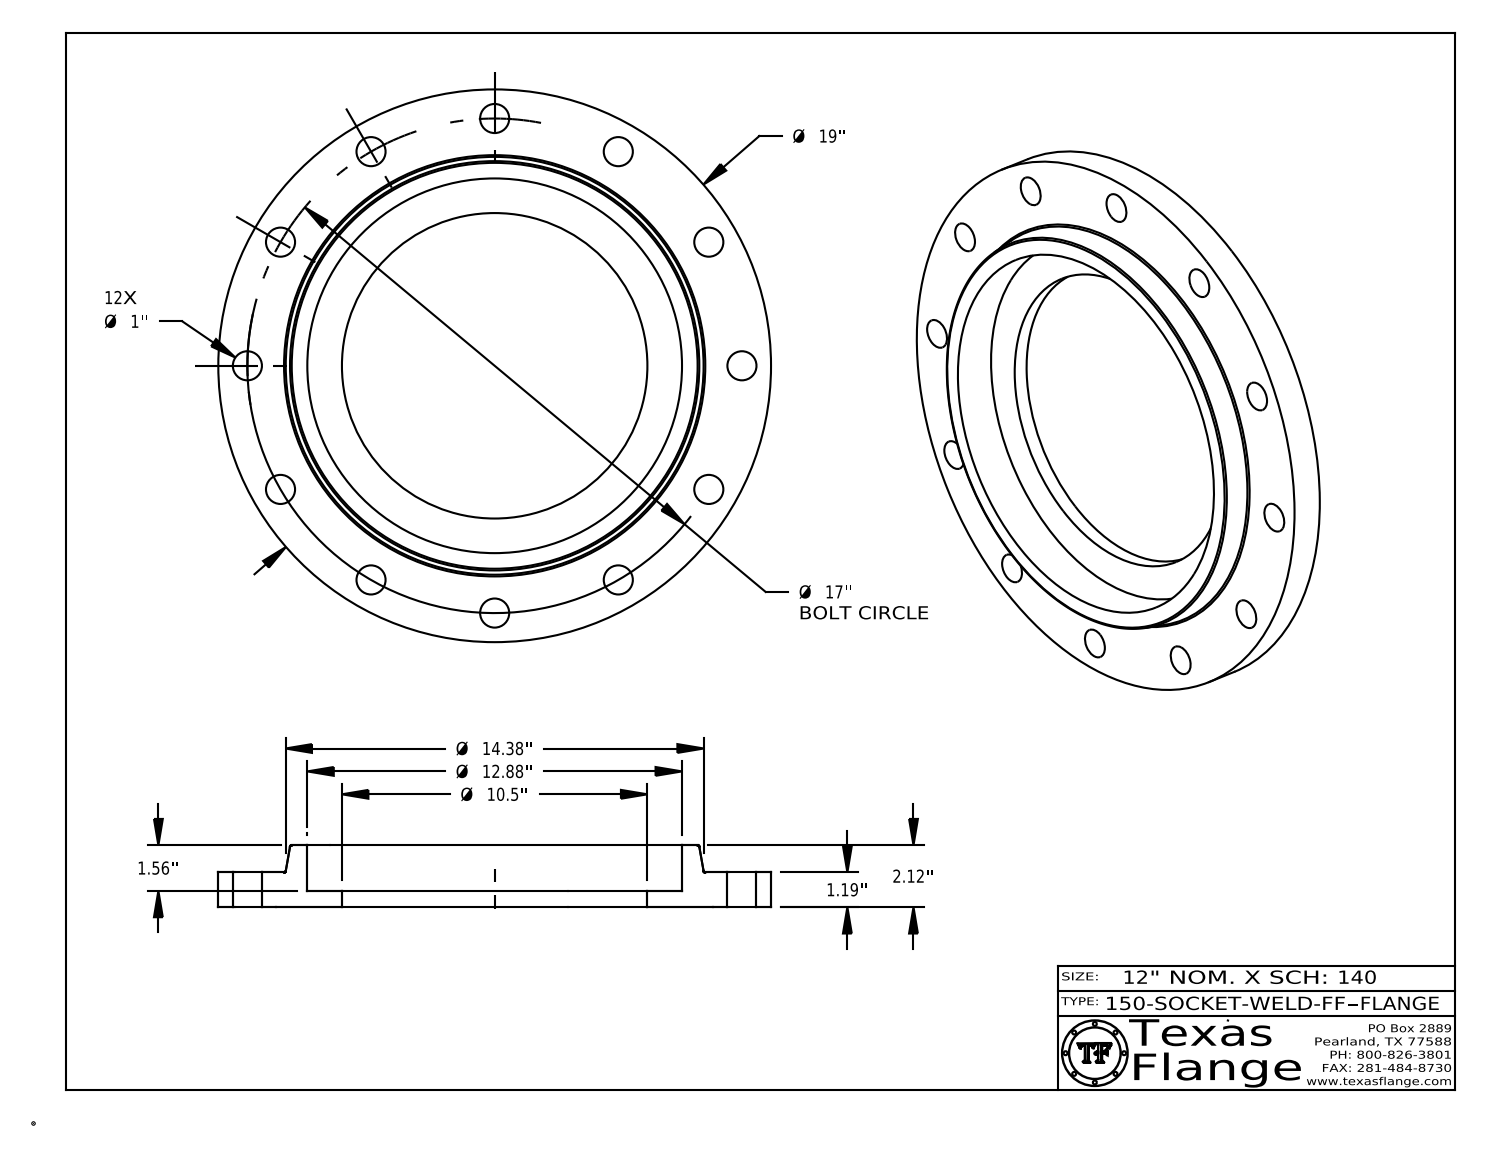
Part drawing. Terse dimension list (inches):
name: 150-SOCKET-WELD-FF
written by: CATIA V5 STEP AP214 (AUTOMOTIVE_DESIGN)
unit: in
bodies: 1 solid, 426 faces (370 planar, 50 cylindrical, 6 other)
size: 19 × 19 × 2.12
volume: 222.1 in³; area: 606 in²
holes: 12× ⌀1, 1× ⌀0.495, 1× ⌀10.5, 1× ⌀12.88
bosses: 8× ⌀0.03, 1× ⌀19, 1× ⌀0.39
face distances: 1.19, 0.56, 0.63, 2.12, 1.56, 0.93, 0.015, 1.175, 0.615, 0.945
hole spacings: 8.5, 16.42, 4.4, 12.02, 14.722, 4.4, 12.021, 14.722
